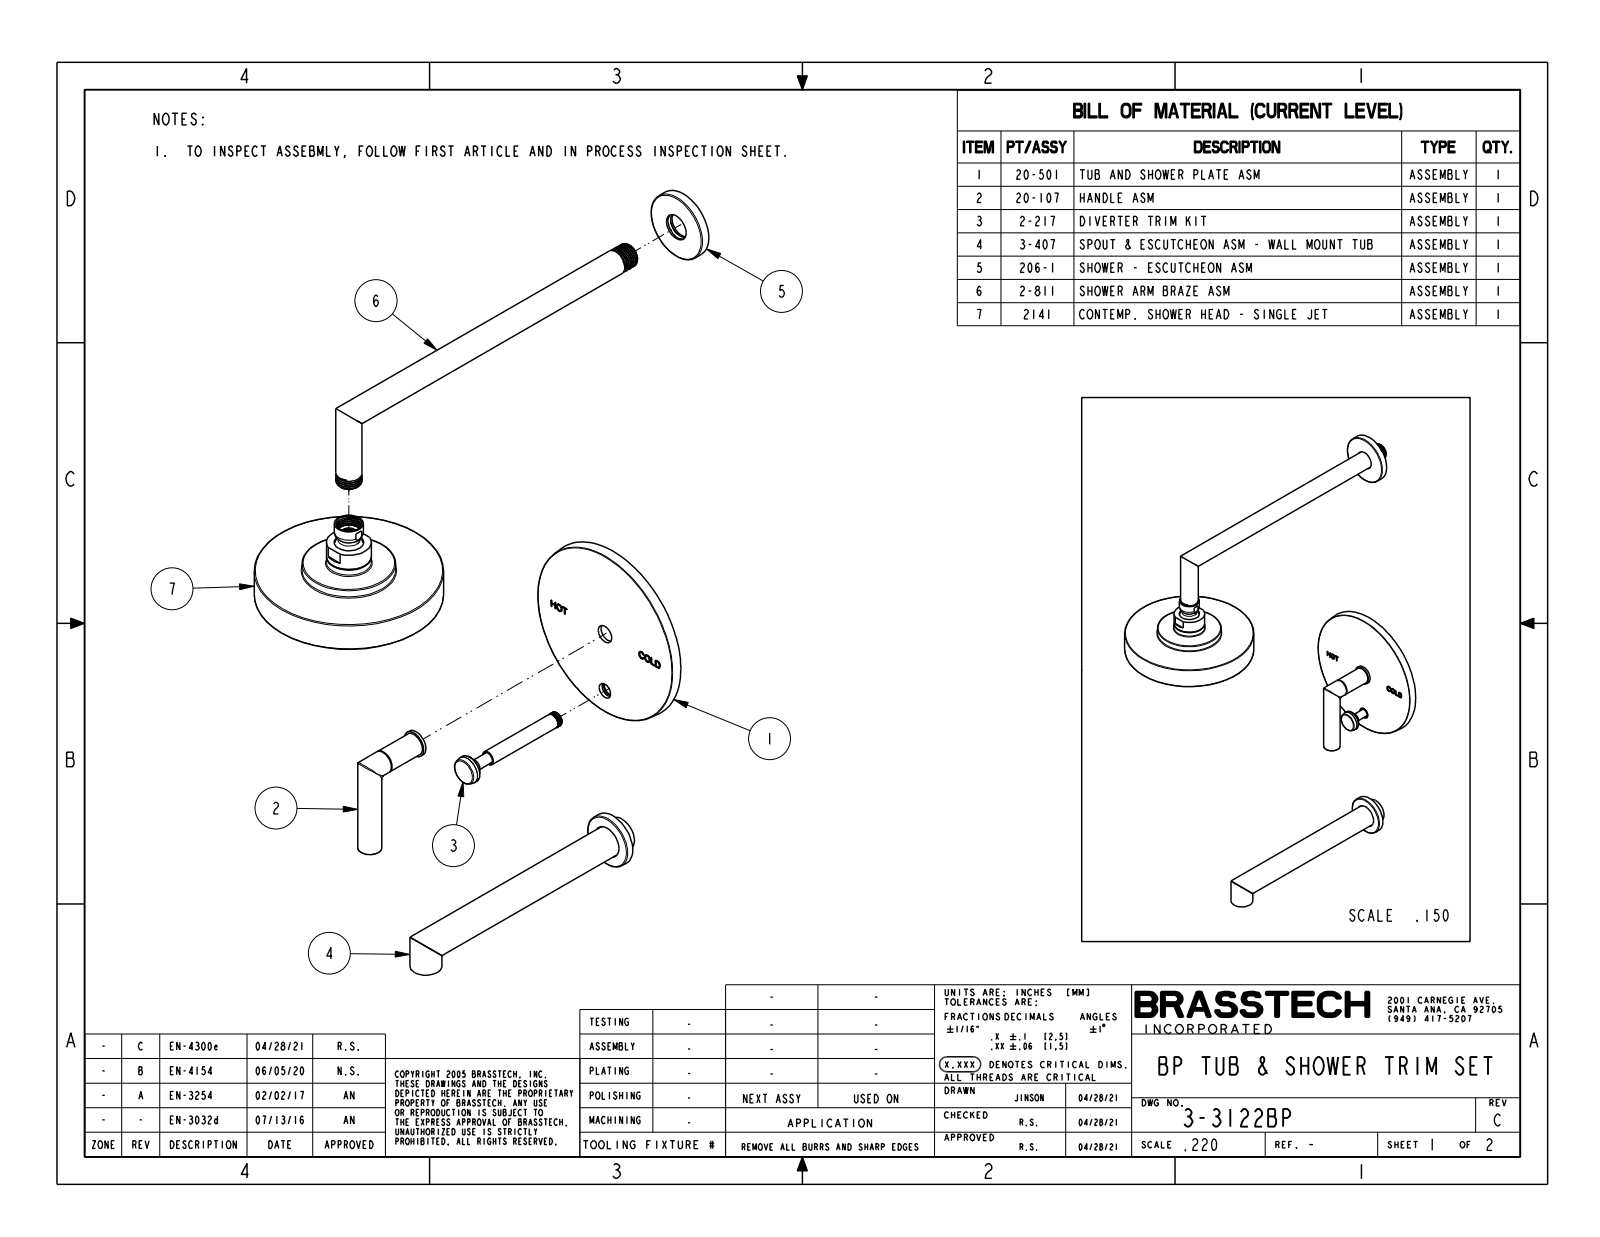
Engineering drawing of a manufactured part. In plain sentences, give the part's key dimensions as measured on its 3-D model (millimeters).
The part is named "3-3122BP". Its 3-D file was written by "CREO PARAMETRIC BY PTC INC, 2018400 (CONFIG_CONTROL_DESIGN)". It is 3 solids with 1026 faces: 166 planar, 224 cylindrical and 636 other. Overall it measures 558.8 by 371 by 152.4 millimeters. Its volume is 1 023 000 cubic millimeters and its surface area 157 400 square millimeters. Round holes: 90 of diameter 1.3, 1 of diameter 5.6, 1 of diameter 133.5. Round bosses or shafts: 2 of diameter 25.4, 2 of diameter 20.7, 2 of diameter 19.1, 1 of diameter 150.1, 1 of diameter 132.6, 1 of diameter 74.2, 1 of diameter 57.2, 1 of diameter 44.5. The main face-to-face distances are 8.9, 7.4, 7.9, 1, 2.5, 6.4, 1.5, 27.5, 20.1, 424.8. The hole center spacings are 21.6, 24.9, 24.9, 43.1, 35.8, 14, 12.9, 14.6.
